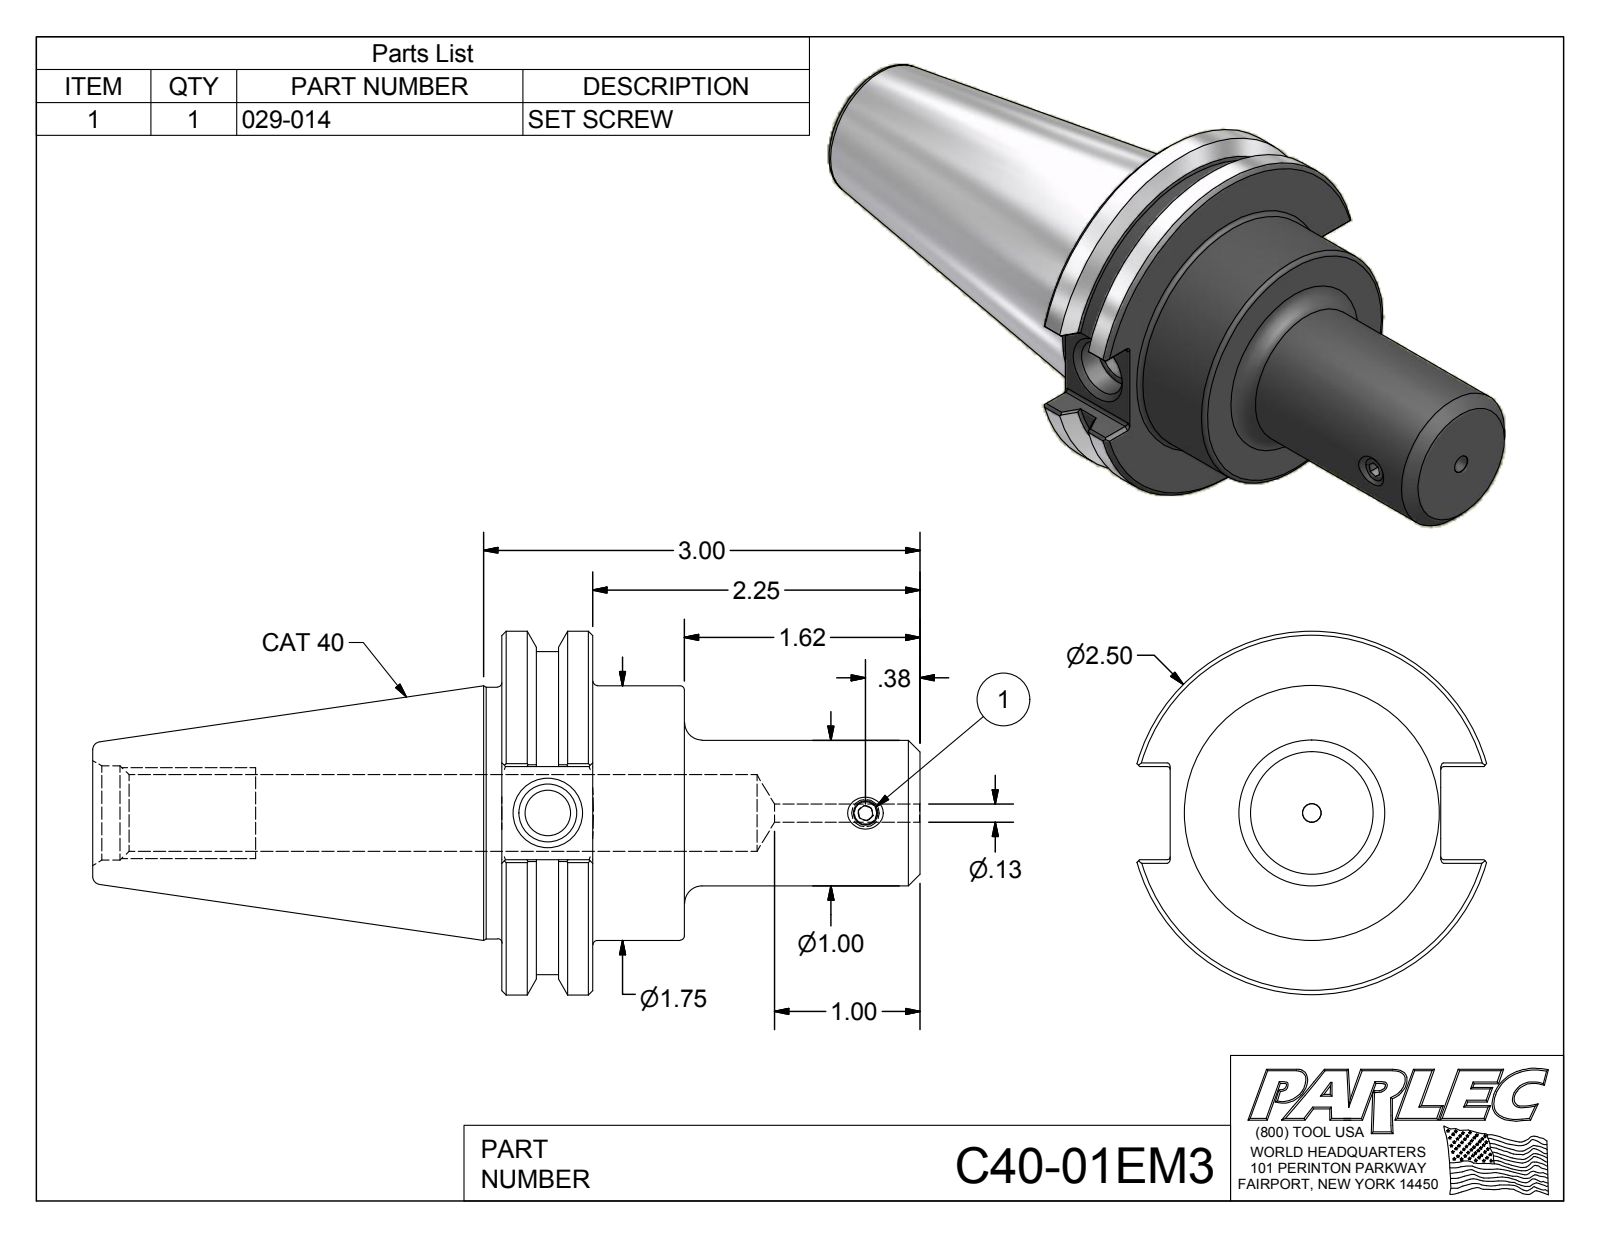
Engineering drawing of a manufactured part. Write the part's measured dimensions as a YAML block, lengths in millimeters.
part_name: "C40-01EM3; C40-01EM3-1; 029-014"
step_written_by: "Autodesk Inventor 2012 (AUTOMOTIVE_DESIGN)"
units: millimeters
bodies: {solids: 2, faces: 104, planar: 41, cylindrical: 28, other: 35}
overall_size: [144.4, 63.5, 61.1]
volume: 141600
surface_area: 27410
round_holes:
  - {diameter: 3.2, count: 1}
  - {diameter: 4, count: 1}
  - {diameter: 8, count: 1}
  - {diameter: 10.1, count: 1}
  - {diameter: 13.4, count: 1}
  - {diameter: 16.5, count: 1}
round_bosses_or_shafts:
  - {diameter: 63.5, count: 1}
  - {diameter: 56.4, count: 1}
  - {diameter: 44.5, count: 1}
  - {diameter: 43.9, count: 1}
  - {diameter: 25.4, count: 1}
  - {diameter: 4.8, count: 1}
partial_cylinders:
  - {radius: 0.5, count: 12}
face_to_face_distances: [15.9, 31.9, 16, 73, 57.2, 41.1, 16.3, 47.2, 71.4, 87.3]
hole_center_spacings: [55.5]
